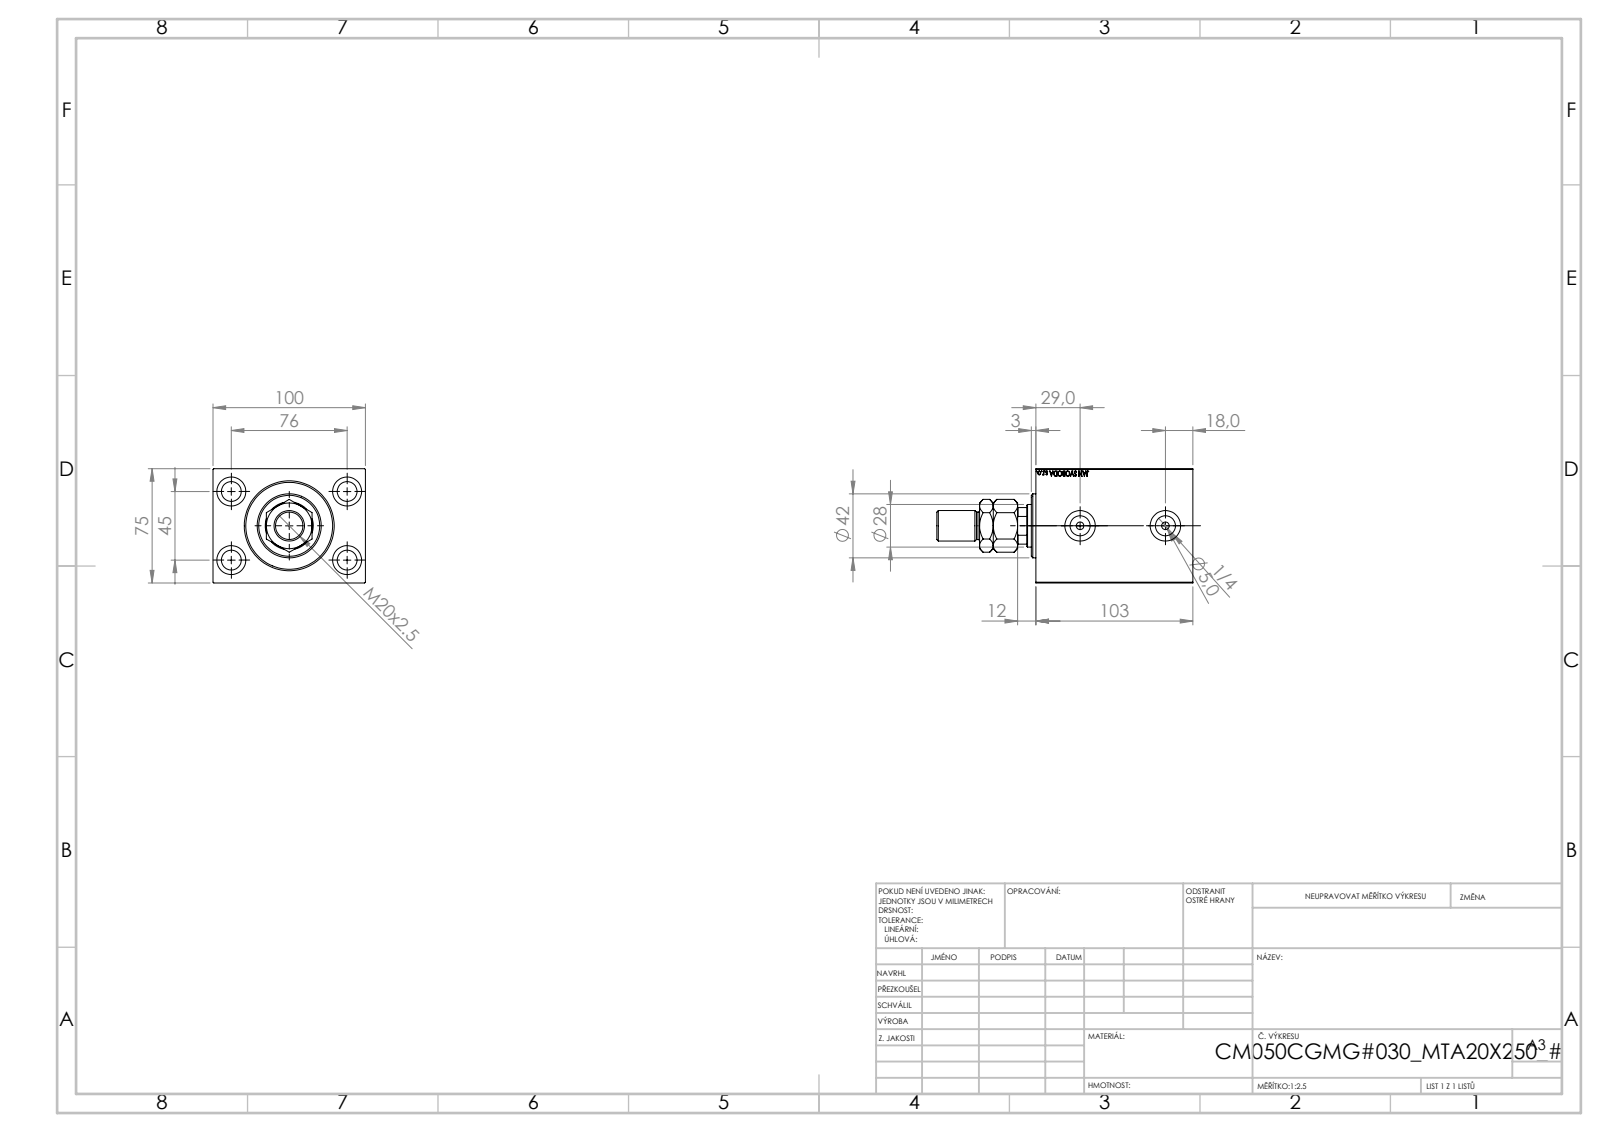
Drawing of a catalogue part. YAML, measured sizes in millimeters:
part_name: "V450CM_C_VCP; MTA; V450CM_C_Body; V450CM_VC_B"
step_written_by: "SolidWorks 2019 (CONFIG_CONTROL_DESIGN)"
units: millimeters
bodies: {solids: 4, faces: 914, planar: 424, cylindrical: 66, other: 424}
overall_size: [168, 100, 75]
volume: 686936
surface_area: 115134
round_holes:
  - {diameter: 13, count: 4}
  - {diameter: 19, count: 4}
  - {diameter: 5, count: 2}
  - {diameter: 13.16, count: 2}
  - {diameter: 20, count: 2}
  - {diameter: 18.5, count: 1}
  - {diameter: 28, count: 1}
  - {diameter: 31.5, count: 1}
  - {diameter: 50, count: 1}
  - {diameter: 52, count: 1}
  - {diameter: 57, count: 1}
round_bosses_or_shafts:
  - {diameter: 42, count: 1}
  - {diameter: 20, count: 1}
  - {diameter: 18, count: 1}
partial_cylinders:
  - {radius: 13.5, count: 1}
face_to_face_distances: [75, 100, 103, 89, 14, 12, 77, 30, 42, 91]
hole_center_spacings: [44.16, 45, 76, 88.32, 56]
